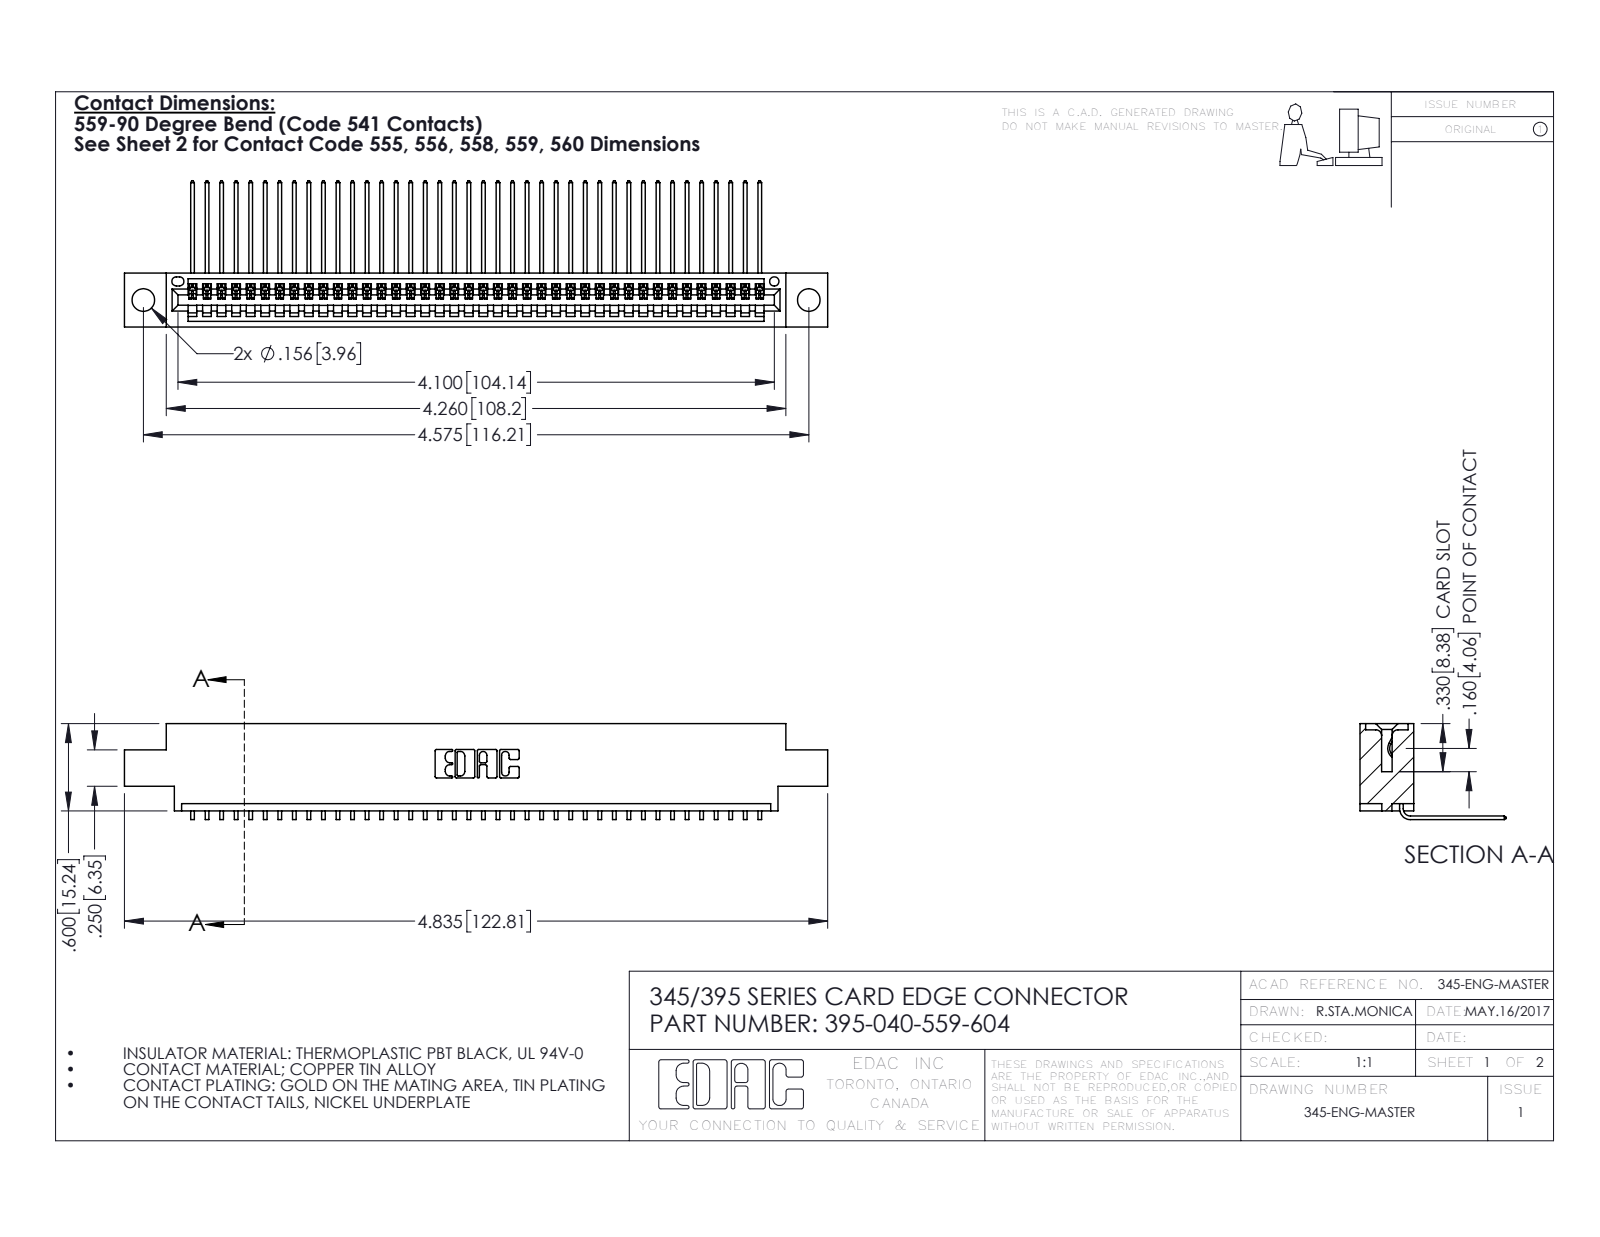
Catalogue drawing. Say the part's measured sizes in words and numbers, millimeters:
The part is named "395-040-559-604; 345-292-001_558 559 Tail - 1; 345 Part_0.170 Offset - 0.156 Dia-TH". Its 3-D file was written by "SolidWorks 2016 (CONFIG_CONTROL_DESIGN)". It is 41 solids with 2530 faces: 1764 planar, 766 cylindrical and 0 other. Overall it measures 122.8 by 25.5 by 16.7 millimeters. Its volume is 11 600 cubic millimeters and its surface area 16 080 square millimeters. Round holes: 2 of diameter 4, 1 of diameter 1.6. Partial cylindrical surfaces (rounded edges, fillets, slot ends): 80 of radius 0.2, 22 of radius 0.3, 6 of radius 0.2, 6 of radius 0.8, 3 of radius 0.7, 2 of radius 0.8, 2 of radius 1, 1 of radius 0.4. The main face-to-face distances are 1.8, 7.6, 9.4, 5.1, 2.5, 6.9, 0.6, 5.7, 4.4, 3.8. The hole center spacings are 6.9, 110.2, 116.2.
